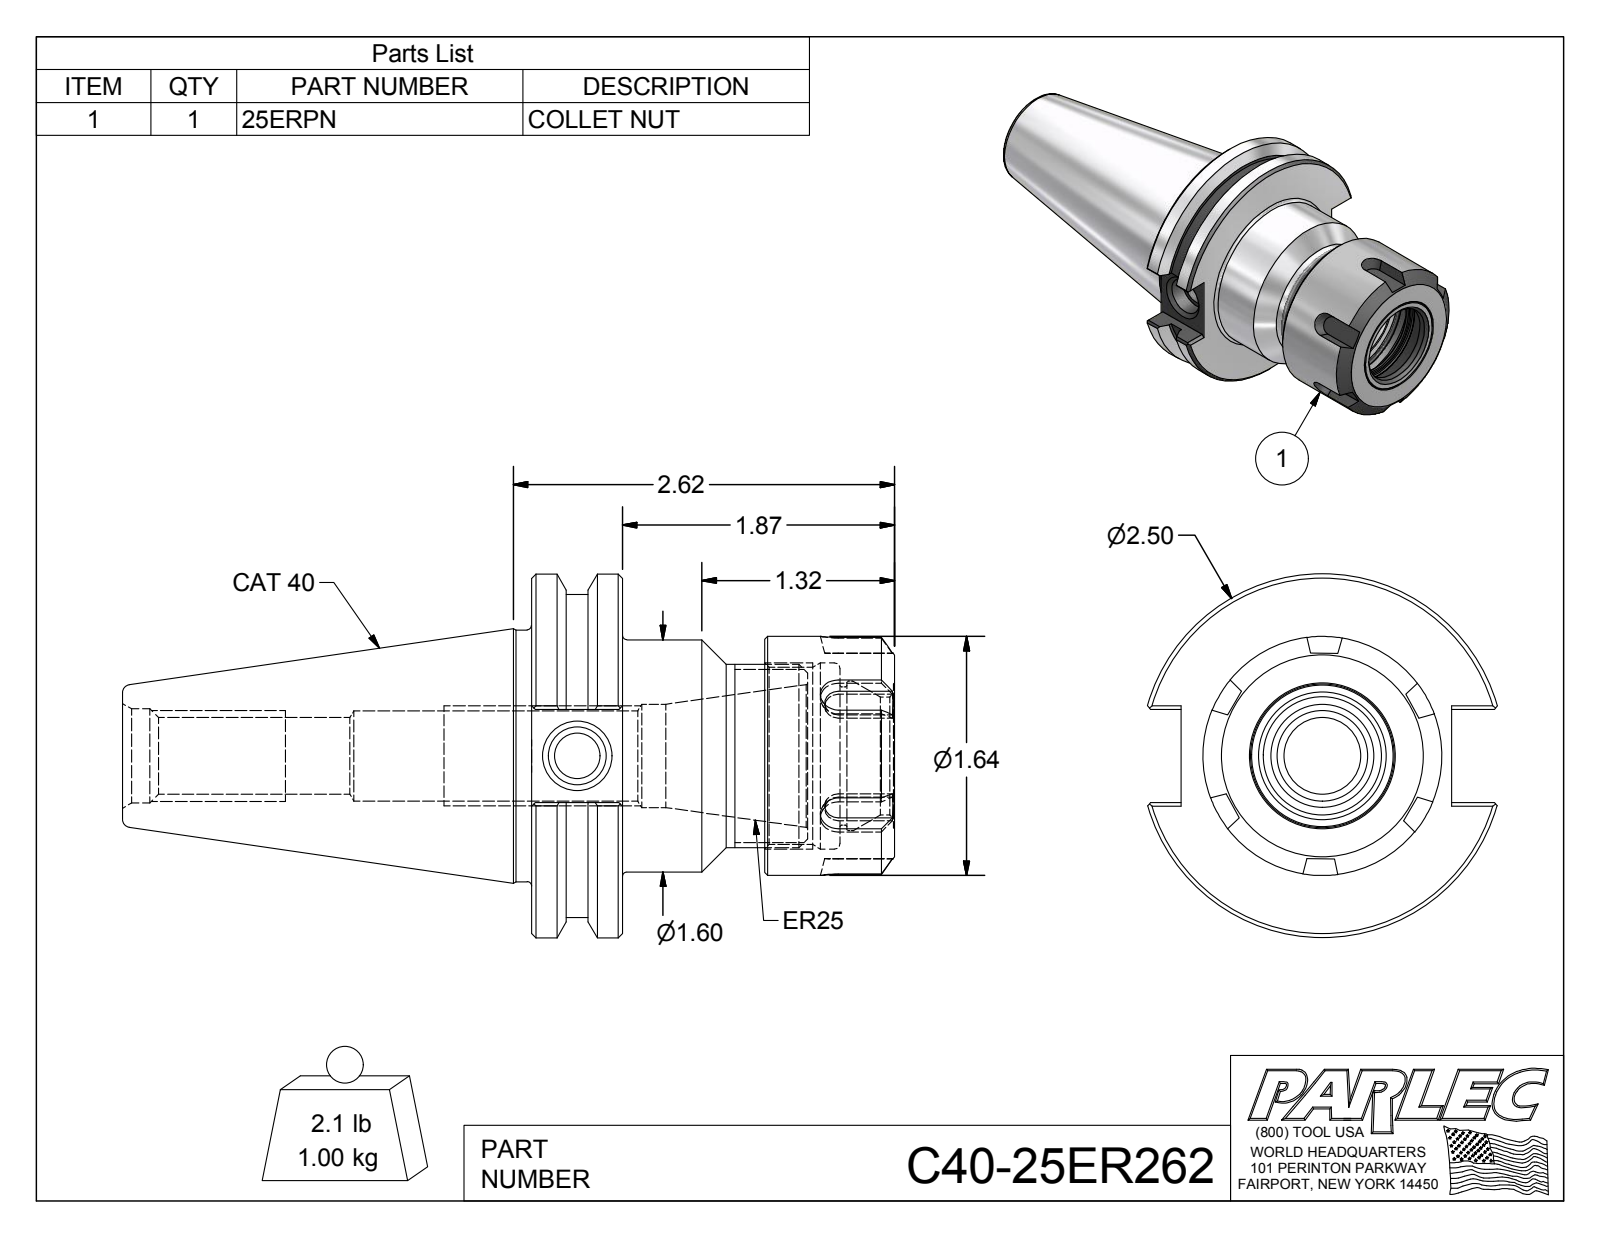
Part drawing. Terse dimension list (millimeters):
name: C40-25ER262; C40-25ER2-1; 25ERPN
written by: Autodesk Inventor 2012 (AUTOMOTIVE_DESIGN)
unit: mm
bodies: 2 solids, 117 faces (54 planar, 21 cylindrical, 42 other)
size: 134.8 × 63.5 × 61
volume: 135 900 mm³; area: 32 660 mm²
holes: 1× ⌀8, 1× ⌀10.1, 1× ⌀13.4, 1× ⌀15.7, 1× ⌀16.5, 1× ⌀18, 1× ⌀20.6, 1× ⌀24.1, 1× ⌀26.1, 1× ⌀30.9, 1× ⌀32.5
bosses: 1× ⌀63.5, 1× ⌀56.4, 1× ⌀43.9, 1× ⌀41.7, 1× ⌀40.5, 1× ⌀32
face distances: 15.9, 63.4, 47.5, 40.7, 24.8, 22.7, 53.8, 38, 13.2, 9.5
